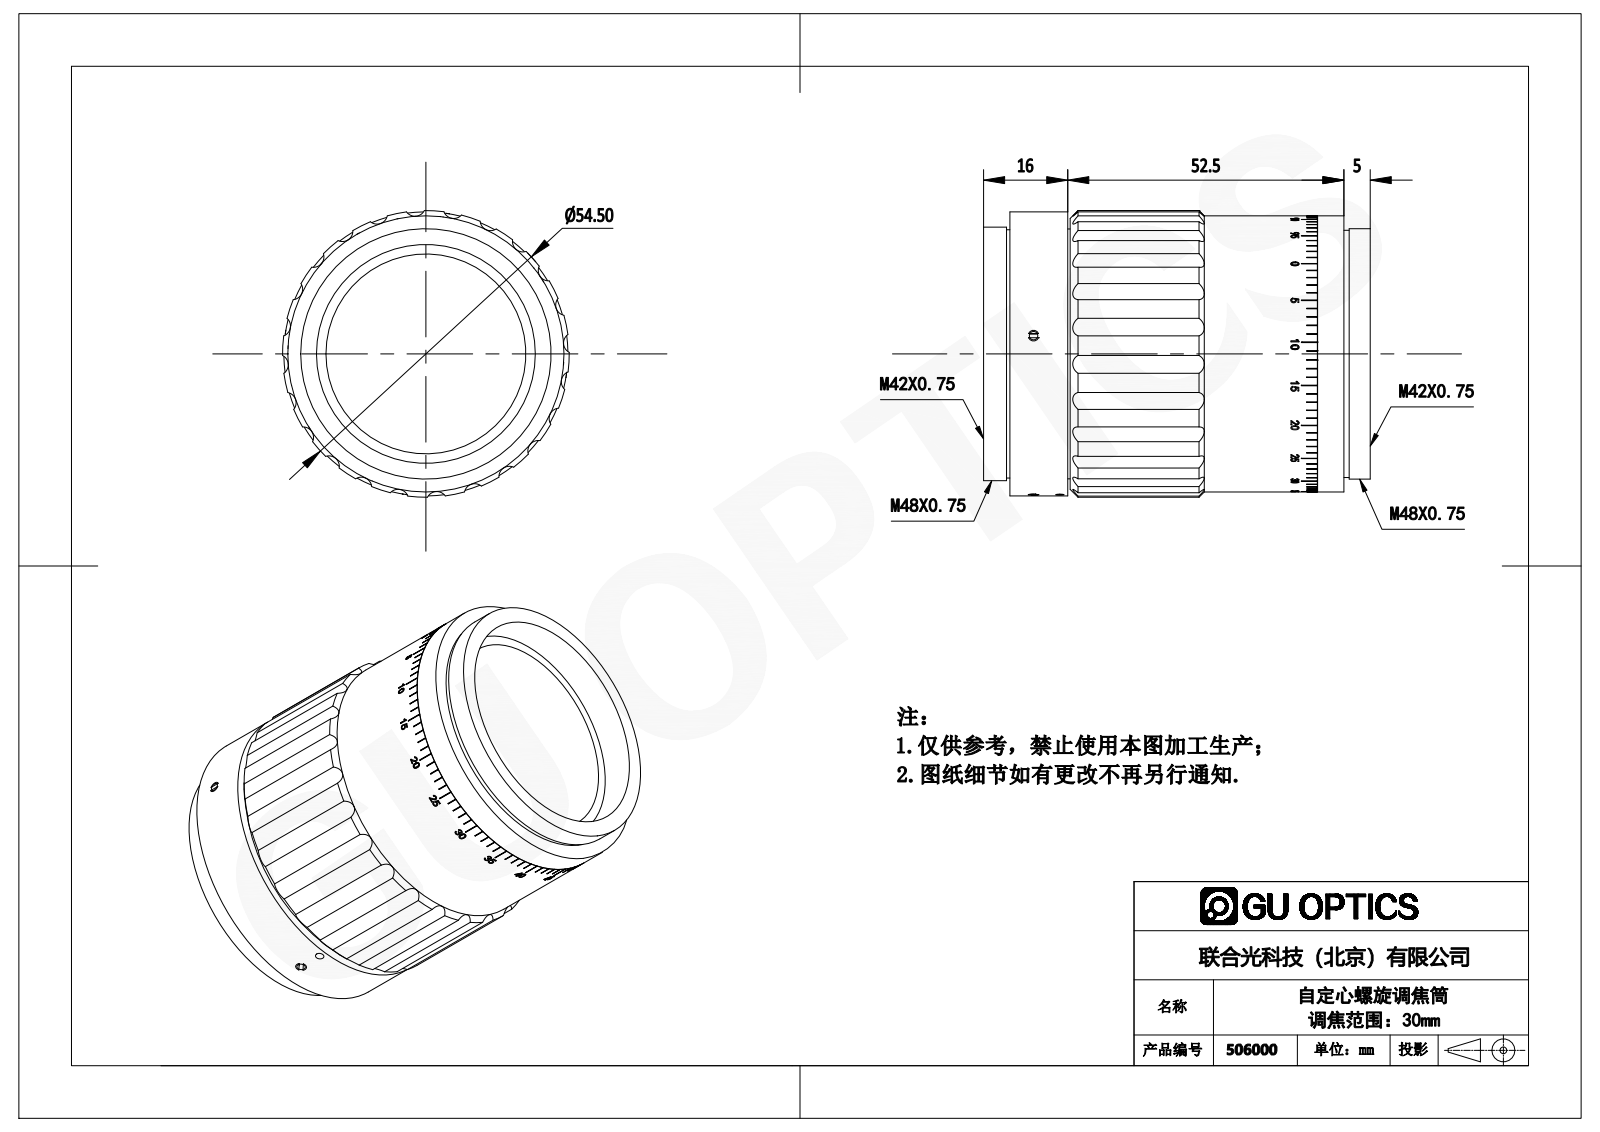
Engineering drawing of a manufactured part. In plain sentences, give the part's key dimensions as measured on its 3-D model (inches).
The part is named "506000自定心连动圈". Its 3-D file was written by "SolidWorks 2016 (AUTOMOTIVE_DESIGN)". It is 8 solids with 1069 faces: 347 planar, 380 cylindrical and 342 other. Overall it measures 2.894 by 2.146 by 2.146 inches. Its volume is 4.183 cubic inches and its surface area 94.21 square inches. Round holes: 5 of diameter 0.063, 3 of diameter 0.083, 1 of diameter 1.496, 1 of diameter 1.614, 1 of diameter 1.638, 1 of diameter 1.732, 1 of diameter 1.752, 1 of diameter 1.76, 1 of diameter 1.878, 1 of diameter 1.949, 1 of diameter 2.008. Round bosses or shafts: 4 of diameter 0.081, 4 of diameter 0.079, 1 of diameter 2.126, 1 of diameter 2.067, 1 of diameter 1.992, 1 of diameter 1.898, 1 of diameter 1.89, 1 of diameter 1.874. Partial cylindrical surfaces (rounded edges, fillets, slot ends): 24 of radius 0.079, 4 of radius 0.876, 3 of radius 0.866, 1 of radius 1.033, 1 of radius 1.073. The main face-to-face distances are 0.197, 0.472, 0.079, 0.394, 2.697, 0.039, 2.5, 2.224, 0.018, 2.01. The hole center spacings are 0.197.
